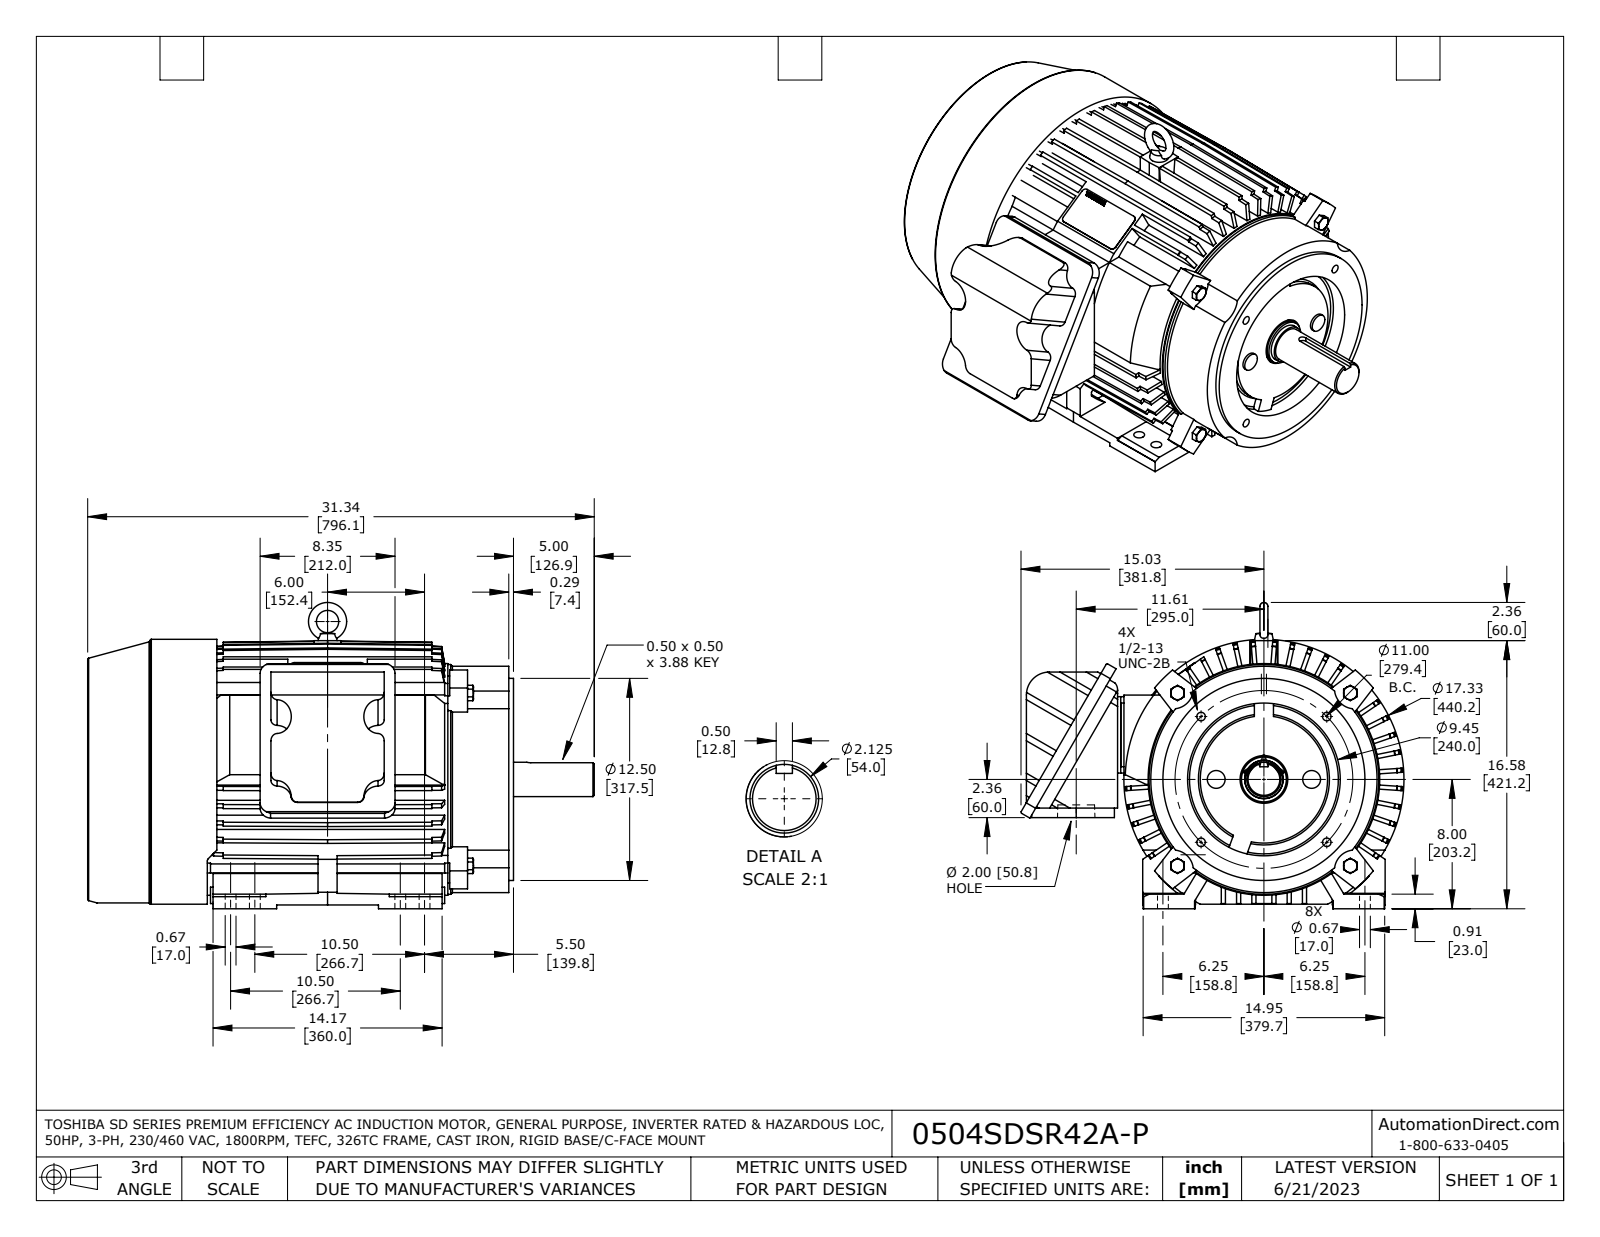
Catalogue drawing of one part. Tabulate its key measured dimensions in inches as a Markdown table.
| quantity | value |
| --- | --- |
| part name | MDSLV005-06-F1-Bottom nc bod broke rep1 |
| STEP written by | SolidWorks 2021 (AUTOMOTIVE_DESIGN) |
| units | inches |
| bodies | 13 solids, 2984 faces (2429 planar, 271 cylindrical, 284 other) |
| overall size | 31.343 × 23.696 × 18.945 |
| volume | 5 638 in³ |
| surface area | 4 824 in² |
| round holes (diameter × count) | 0.354 × 8, 0.669 × 8, 0.087 × 4, 0.398 × 4, 0.527 × 4, 0.551 × 4, 0.472 × 1, 0.545 × 1, 1.26 × 1, 2.382 × 1, 2.398 × 1, 2.756 × 1 |
| round bosses / shafts (diameter × count) | 1.102 × 2, 17.331 × 1, 14.331 × 1, 14.213 × 1, 14 × 1, 13.819 × 1, 12.5 × 1, 7.874 × 1 |
| partial cylindrical surfaces (radius × count) | 0.394 × 26, 0.021 × 6, 0.042 × 6, 0.055 × 6, 0.906 × 6, 0.02 × 4, 0.09 × 4, 0.25 × 4 |
| main face-to-face distances | 0.256, 0.591, 14.882, 14.291, 0.283, 14.598, 14.008, 0.256, 7.992, 0.256 |
| hole center spacings | 8.816, 9.348, 10.228, 0.669, 1.39, 1.5, 2.059, 2.363 |
